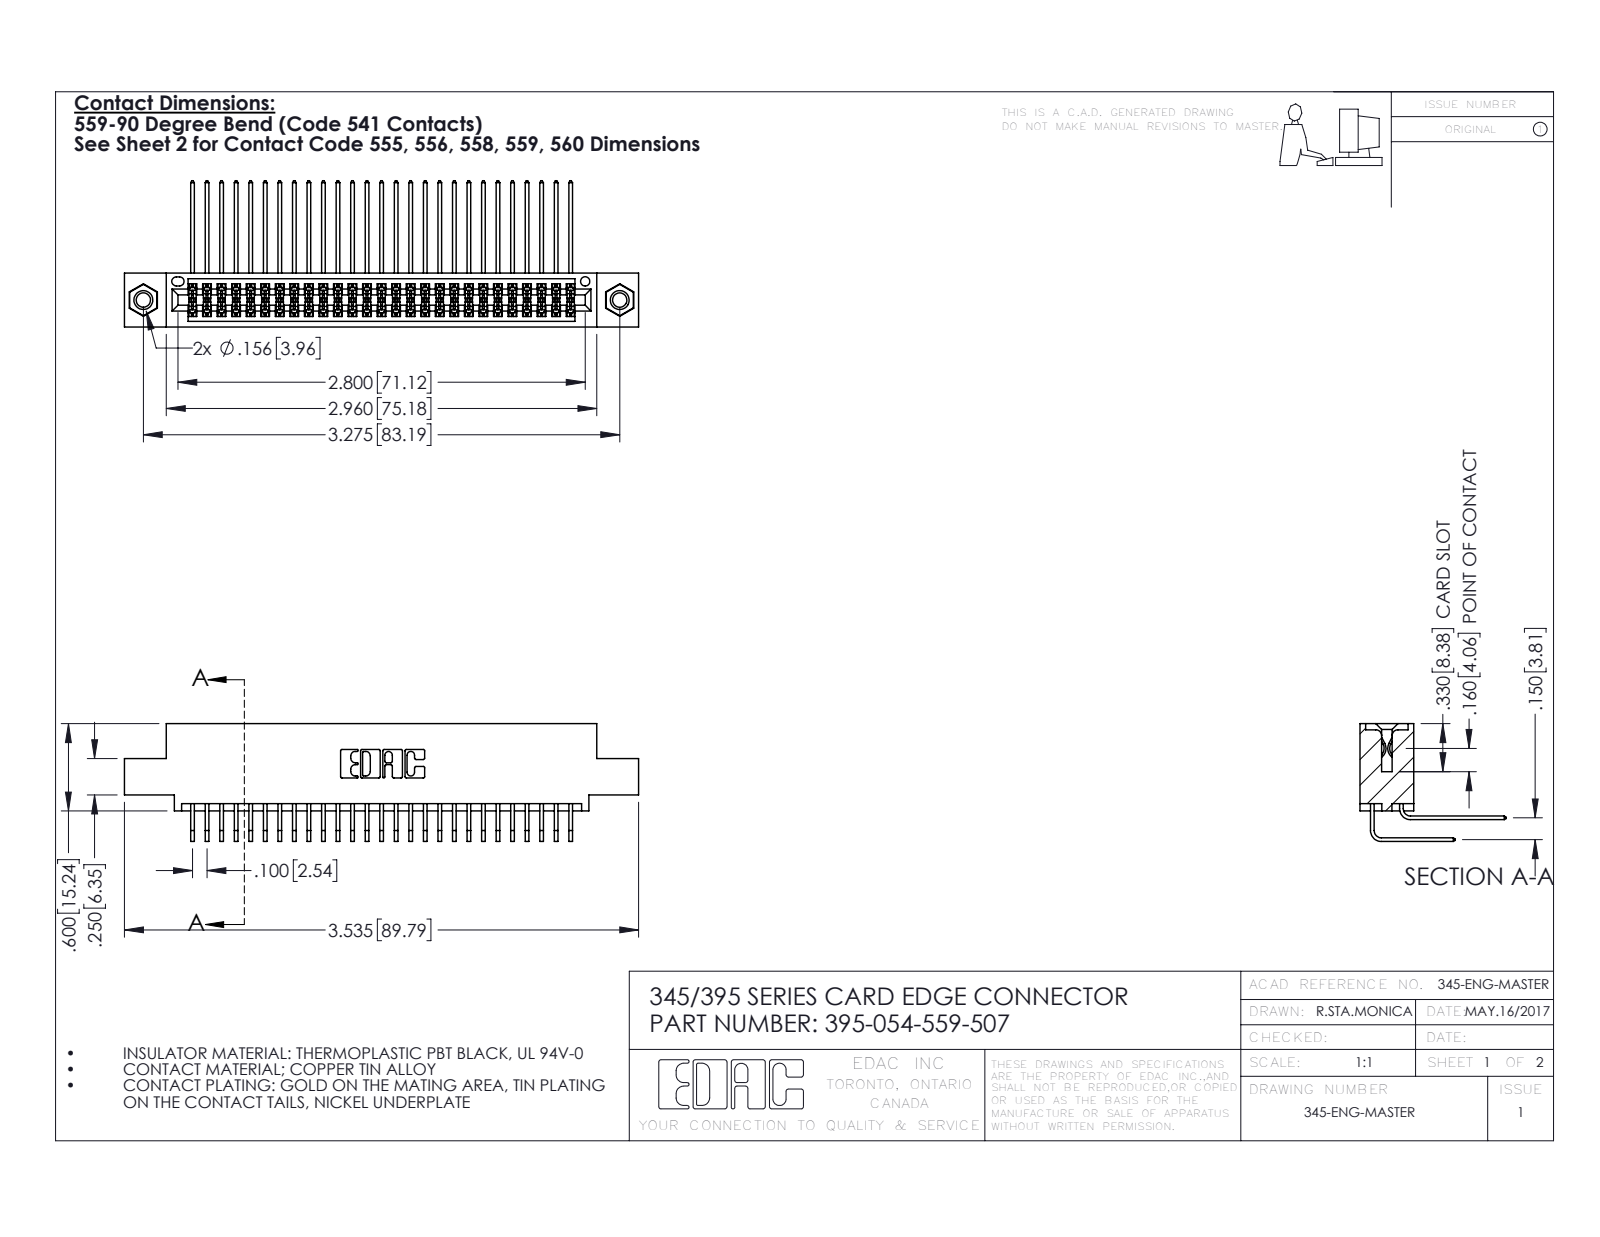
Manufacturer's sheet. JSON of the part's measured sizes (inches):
{"part_name": "345 Part_0.110 Offset - 0.156 Dia-TI; 345-250-001_345-250-005-103; 395-054-559-507; 345-292-001_558 559 Tail - 1 (+1 more)", "step_written_by": "SolidWorks 2016 (CONFIG_CONTROL_DESIGN)", "units": "inches", "bodies": {"solids": 57, "faces": 2998, "planar": 2006, "cylindrical": 976, "other": 16}, "overall_size": [3.535, 1.005, 0.809], "volume_in3": 0.537, "surface_area_in2": 22.19, "round_holes": [[0.098, 2], [0.125, 2], [0.156, 2], [0.064, 1]], "round_bosses_or_shafts": [[0.155, 2]], "partial_cylinders_radius": [[0.006, 81], [0.01, 22], [0.007, 6], [0.031, 6], [0.026, 3], [0.014, 2], [0.019, 2], [0.022, 2]], "face_to_face_distances": [0.072, 0.298, 0.2, 0.37, 0.098, 0.272, 0.025, 0.225, 0.15, 0.175], "hole_center_spacings": [0.27, 3.04, 3.275]}
